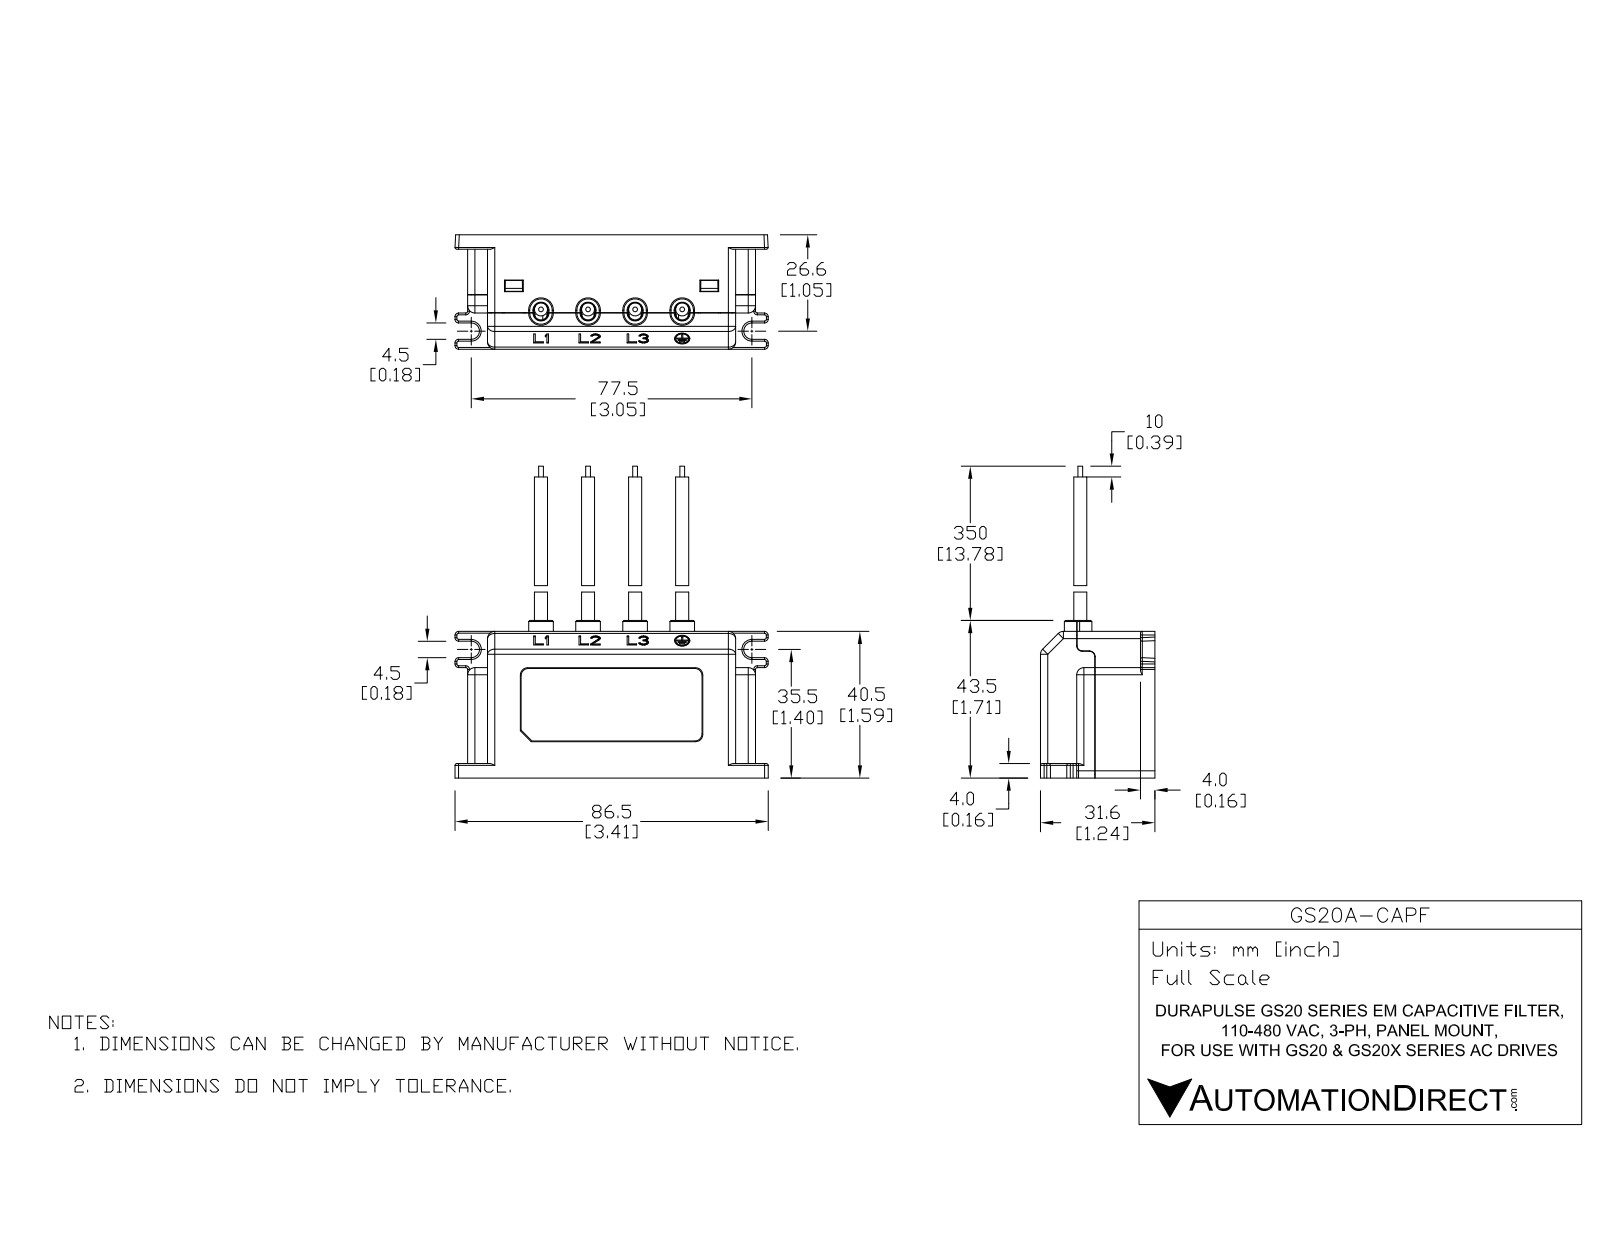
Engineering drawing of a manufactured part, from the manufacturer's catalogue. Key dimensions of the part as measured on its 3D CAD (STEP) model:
Part name (STEP PRODUCT): CXY101-43A-PD-3D00 b1
STEP written by: SolidWorks 2017 (AUTOMOTIVE_DESIGN)
Units: inches
Bodies: 7 solids, 1049 faces (641 planar, 125 cylindrical, 283 other)
Overall size (bounding box): 3.406 × 3.272 × 1.244
Volume: 1.673 in³ · Surface area: 51.39 in²
Round holes (diameter × count): ⌀0.177 ×1
Round bosses / shafts (diameter × count): ⌀0.146 ×8
Partial cylindrical surfaces — rounded edges, fillets, slot ends (radius × count): R0.079 ×26, R0.039 ×16, R0.059 ×13, R0.02 ×11, R0.047 ×8, R0.008 ×4, R0.118 ×4, R0.138 ×4
Main face-to-face distances: 0.079, 1.165, 1.157, 0.071, 1.087, 1.236, 1.594, 1.244, 1.445, 1.243
